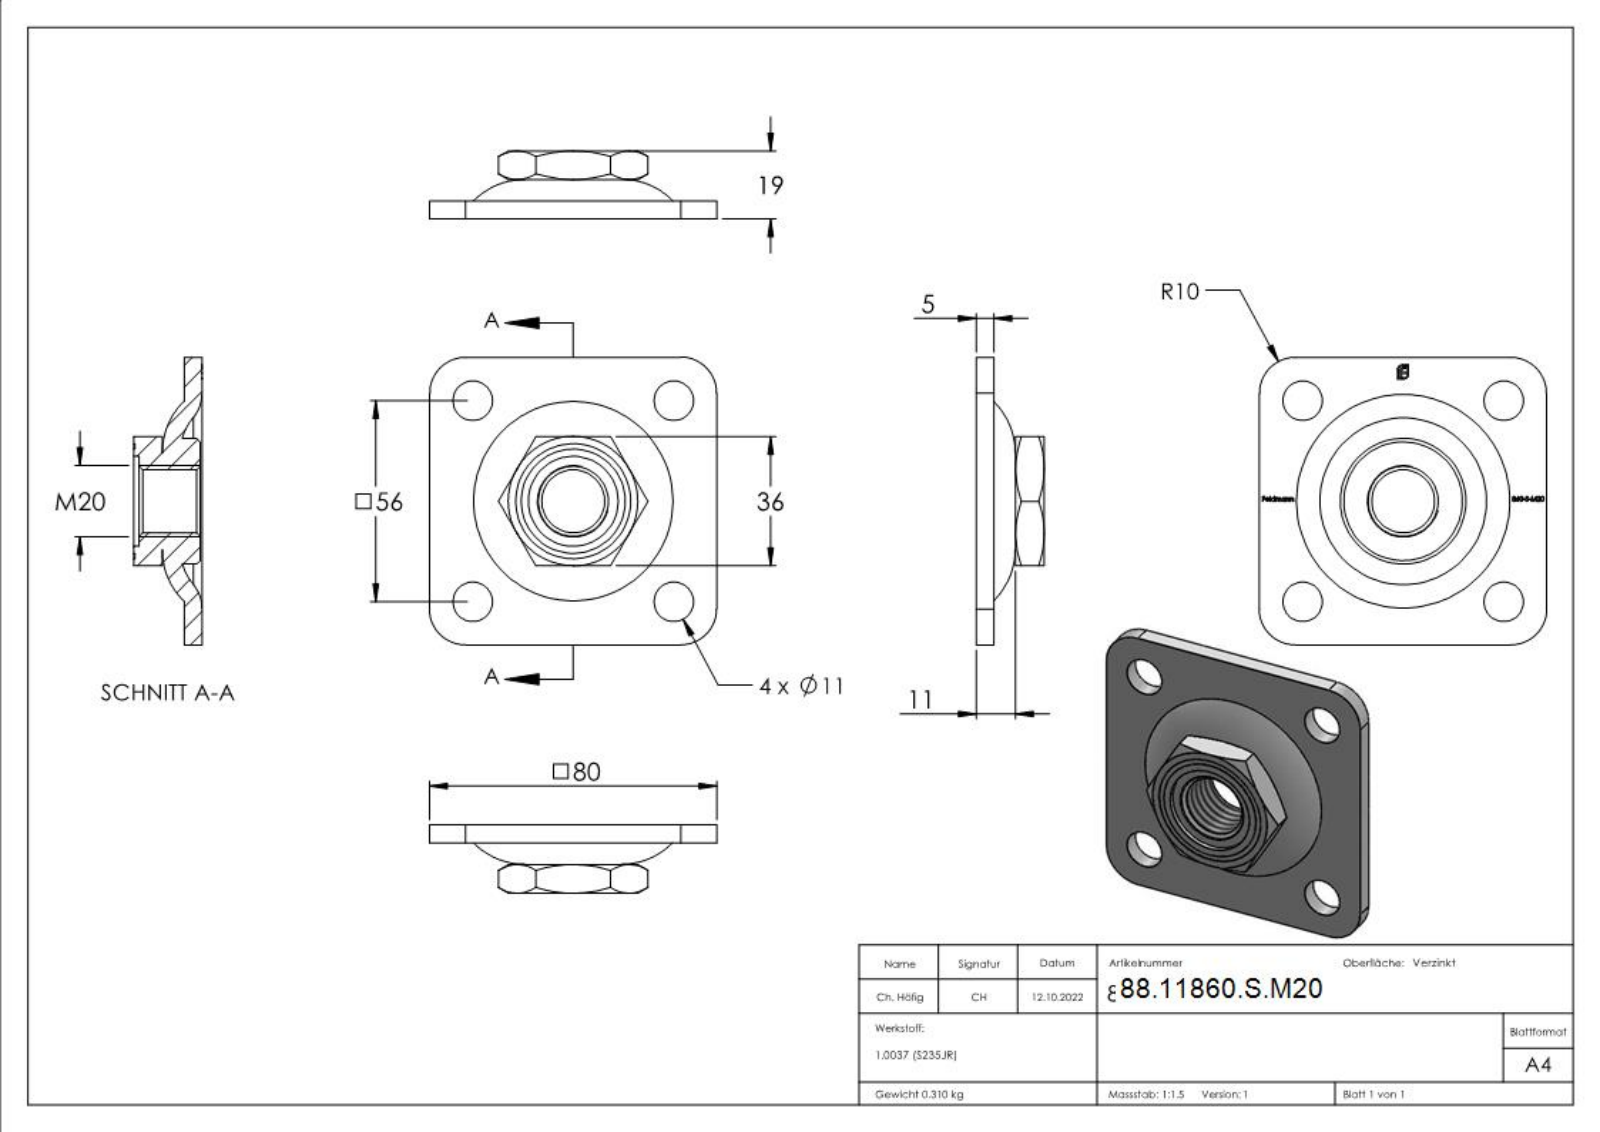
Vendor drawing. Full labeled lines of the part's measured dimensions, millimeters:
Part name (STEP PRODUCT): 860-S-M20
STEP written by: SolidWorks 2018 (CONFIG_CONTROL_DESIGN)
Units: millimetres
Bodies: 1 solid, 316 faces (152 planar, 13 cylindrical, 151 other)
Overall size (bounding box): 80 × 80 × 19
Volume: 39 761 mm³ · Surface area: 17 578 mm²
Round holes (diameter × count): ⌀11 ×4, ⌀17.5 ×1, ⌀25 ×1, ⌀32 ×1
Round bosses / shafts (diameter × count): ⌀35 ×1, ⌀29 ×1
Partial cylindrical surfaces — rounded edges, fillets, slot ends (radius × count): R10 ×4
Main face-to-face distances: 5, 80, 0.5, 4.5, 6, 11, 10.5, 36, 19, 18.5
Hole centre spacings: 39.6, 56, 79.2
